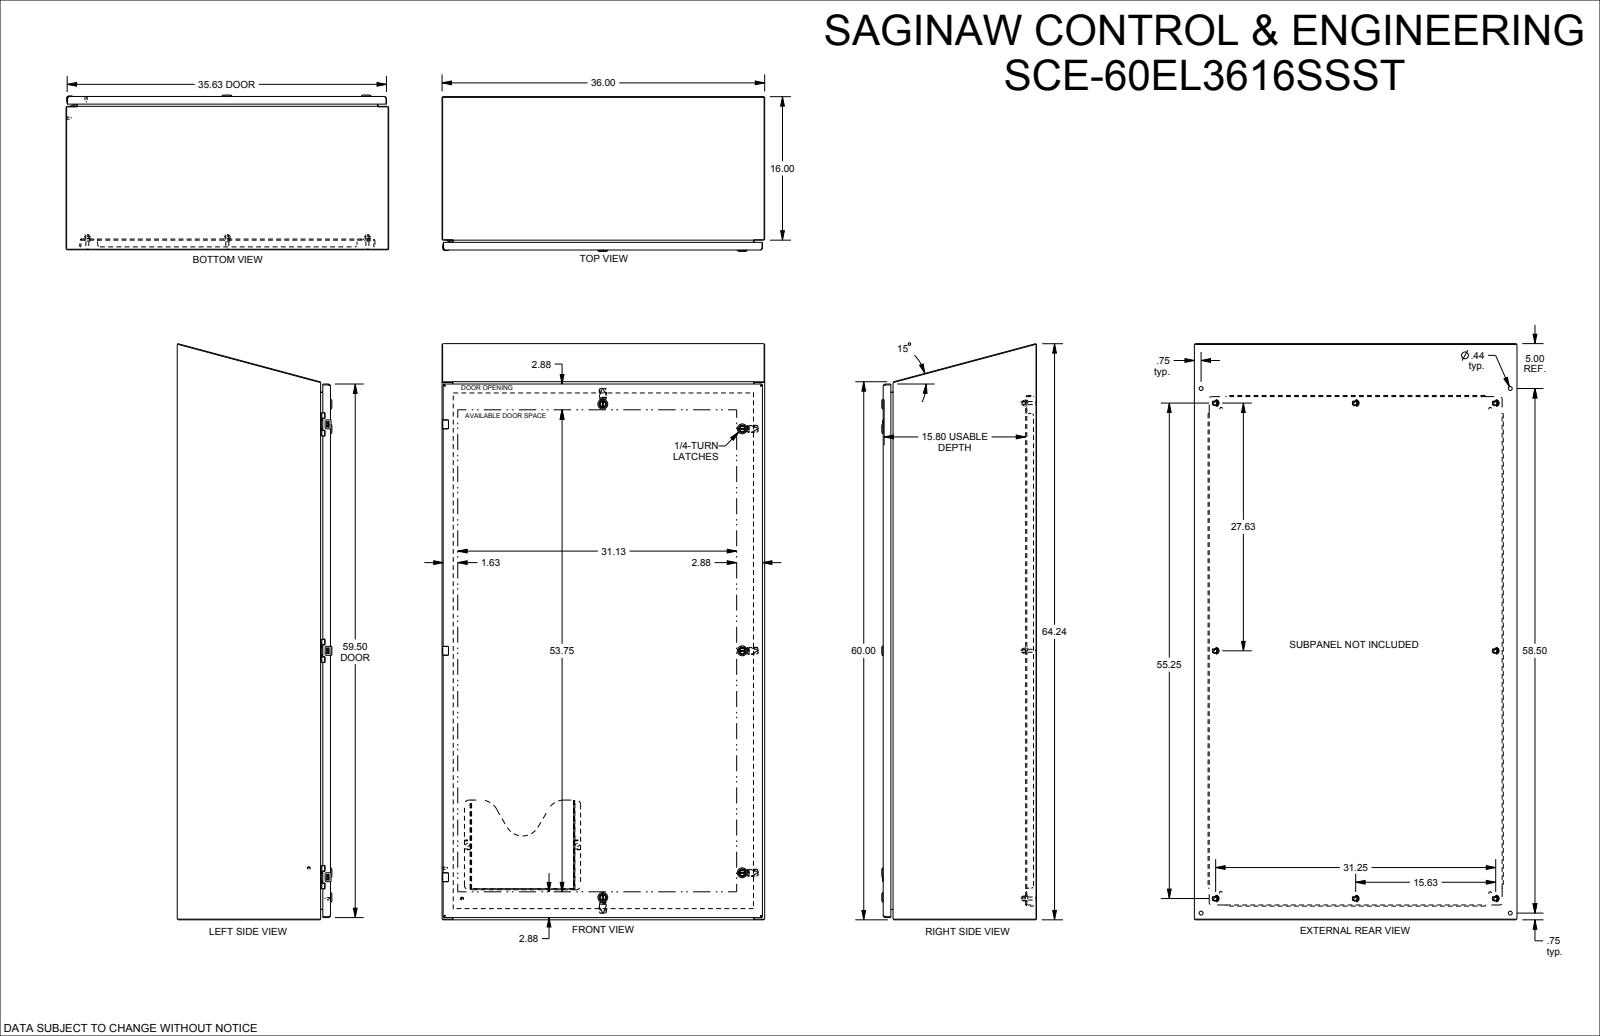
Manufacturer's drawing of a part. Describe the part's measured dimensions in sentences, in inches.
The part is named "SCE-60EL3616SSST". Its 3-D file was written by "SolidWorks 2019 (CONFIG_CONTROL_DESIGN)". It is 0 solids with 4763 faces: 2328 planar, 1314 cylindrical and 1121 other. Overall it measures 64.253 by 36 by 17.256 inches. Round holes: 8 of diameter 0.367, 8 of diameter 0.5, 6 of diameter 0.172, 6 of diameter 0.205, 6 of diameter 0.244, 6 of diameter 0.266, 6 of diameter 0.375, 5 of diameter 0.197, 5 of diameter 0.315, 5 of diameter 0.394, 5 of diameter 0.634, 4 of diameter 0.281. Round bosses or shafts: 9 of diameter 0.17, 8 of diameter 0.366, 8 of diameter 0.332, 6 of diameter 0.25, 5 of diameter 1.102, 5 of diameter 0.866, 5 of diameter 0.802, 5 of diameter 0.78. Partial cylindrical surfaces (rounded edges, fillets, slot ends): 142 of radius 0.012, 52 of radius 0.02, 50 of radius 0.01, 43 of radius 0.015, 23 of radius 0.04, 20 of radius 0.157, 16 of radius 0.03, 13 of radius 0.07. The main face-to-face distances are 0.075, 0.075, 16.995, 16.92, 0.104, 17.099, 17.024, 1.125, 35.925, 15.795. The hole center spacings are 25.25, 50.5, 0.049, 0.986, 24.265, 25.25, 25.25, 26.235.
